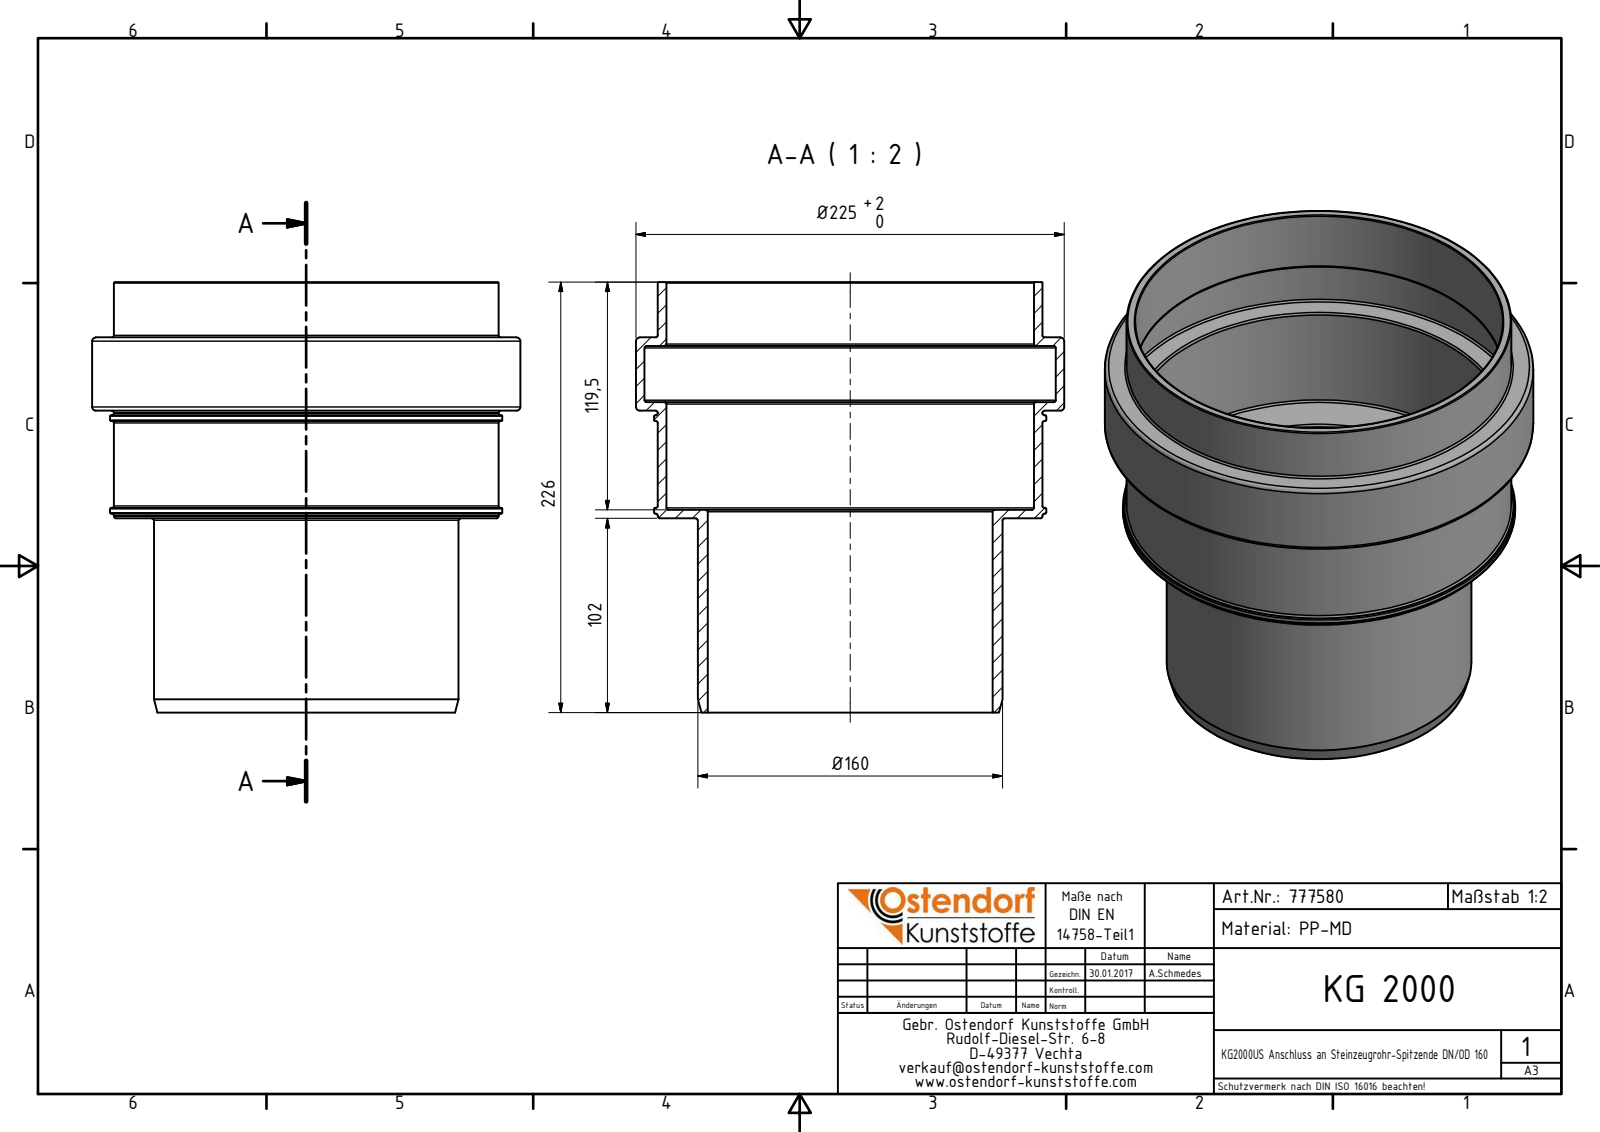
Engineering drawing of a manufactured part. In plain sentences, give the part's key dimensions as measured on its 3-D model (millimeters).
The part is named "777580 KG2000US Anschluss an Steinzeugrohr-Spitzende DN_OD 160". Its 3-D file was written by "Autodesk Inventor 2016 (AUTOMOTIVE_DESIGN)". It is 1 solid with 47 faces: 12 planar, 12 cylindrical and 23 other. Overall it measures 226 by 225 by 225 millimeters. Its volume is 739 578 cubic millimeters and its surface area 315 156 square millimeters. Round holes: 1 of diameter 149.6, 1 of diameter 193, 1 of diameter 216. Round bosses or shafts: 1 of diameter 225, 1 of diameter 206, 1 of diameter 202, 1 of diameter 160. The main face-to-face distances are 4.5, 90.5, 56.5, 34, 86, 61, 29.5, 95, 52, 38.5.
